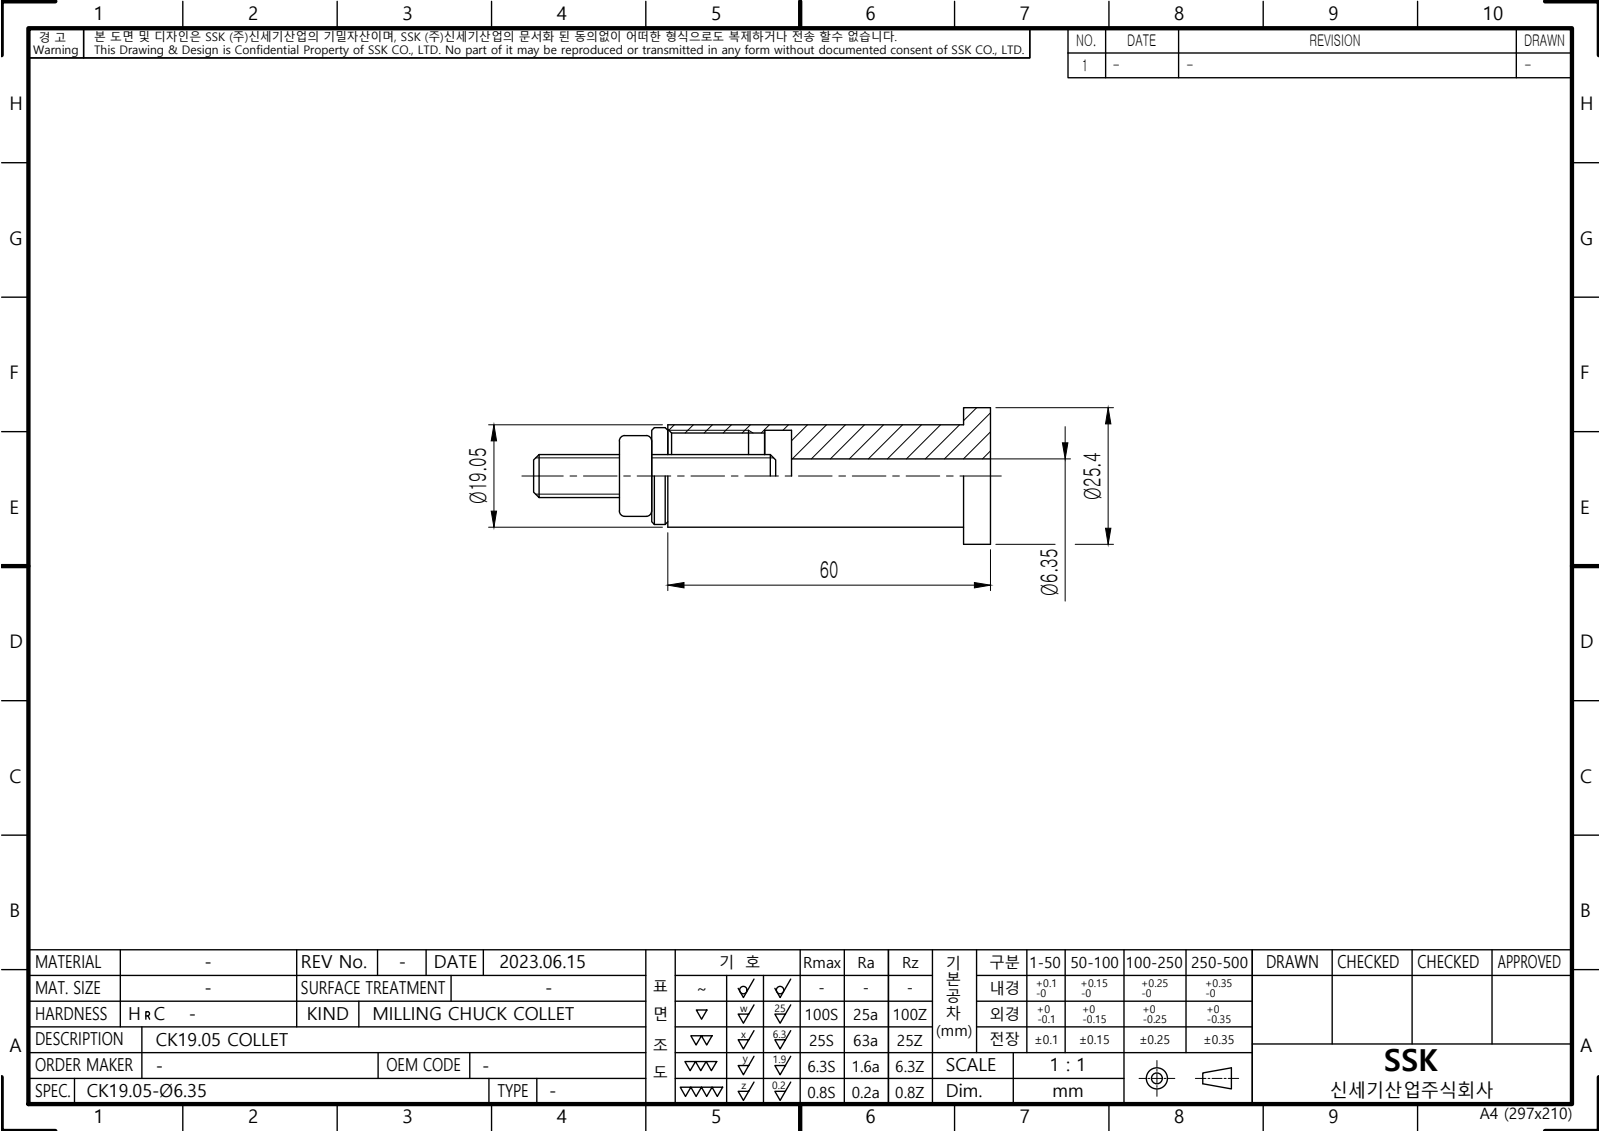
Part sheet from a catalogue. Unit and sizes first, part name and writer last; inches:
Units: inches
Overall size (bounding box): 2.362 × 1 × 1
Round holes (diameter × count): ⌀0.25 ×1, ⌀0.627 ×1, ⌀0.669 ×1
Round bosses / shafts (diameter × count): ⌀1 ×1, ⌀0.75 ×1
Main face-to-face distances: 0.197, 1.457, 1.26, 0.906, 2.165, 2.362, 0.709, 1.654
Volume: 0.752 in³ · Surface area: 10.23 in²
Bodies: 1 solid, 10 faces (5 planar, 5 cylindrical, 0 other)
Part name (STEP PRODUCT): LO-CK19.05-6.35
STEP written by: Autodesk Inventor 2022 (AUTOMOTIVE_DESIGN)
